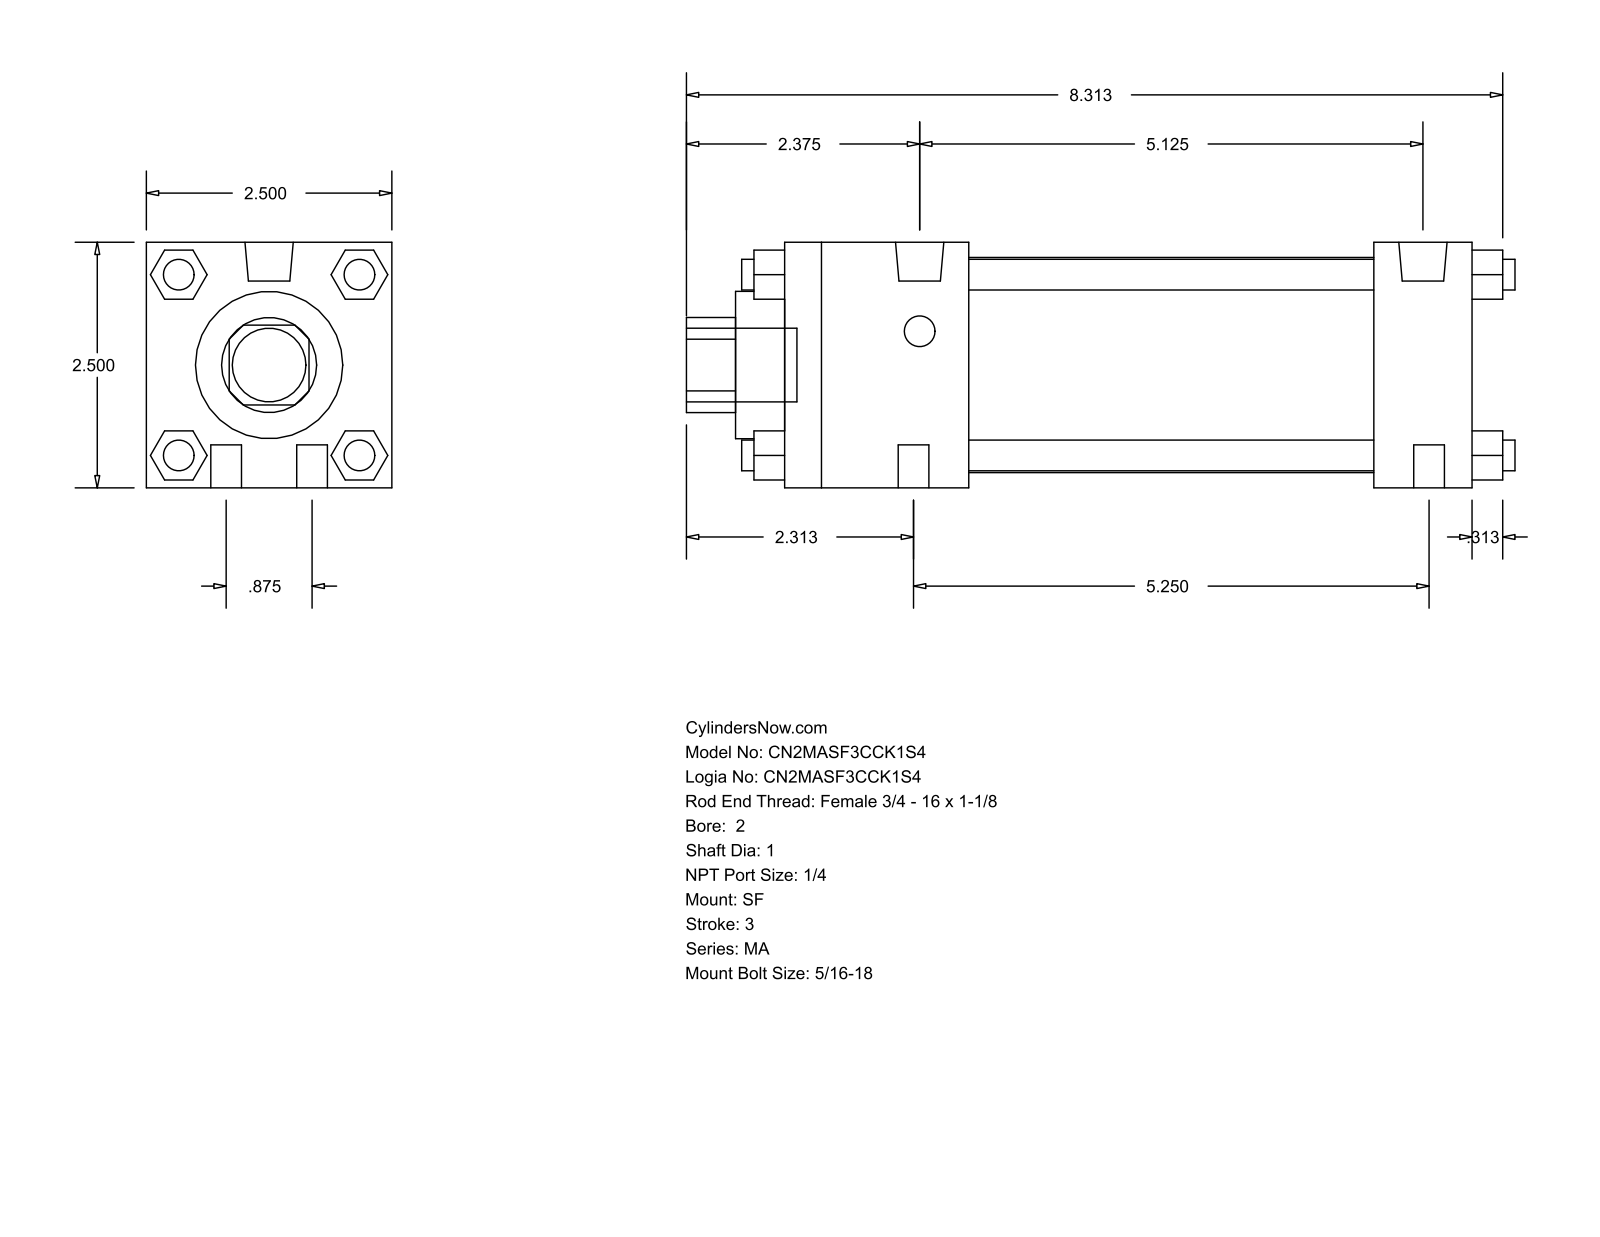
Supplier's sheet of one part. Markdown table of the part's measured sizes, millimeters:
| quantity | value |
| --- | --- |
| part name | MA_SF__0200_1 |
| STEP written by | GSSL Pune (CONFIG_CONTROL_DESIGN) |
| units | millimeters |
| bodies | 0 solids, 124 faces (94 planar, 30 cylindrical, 0 other) |
| overall size | 214.31 × 63.5 × 63.5 |
| round holes (diameter × count) | 25.4 × 1, 38.1 × 1, 55.63 × 1 |
| round bosses / shafts (diameter × count) | 7.94 × 10, 12.49 × 2, 19.05 × 1 |
| partial cylindrical surfaces (radius × count) | 12.29 × 1 |
| main face-to-face distances | 63.5, 177.8, 12.7, 25.4, 152.4, 47.63, 104.77, 130.17, 40.47, 23.37 |
